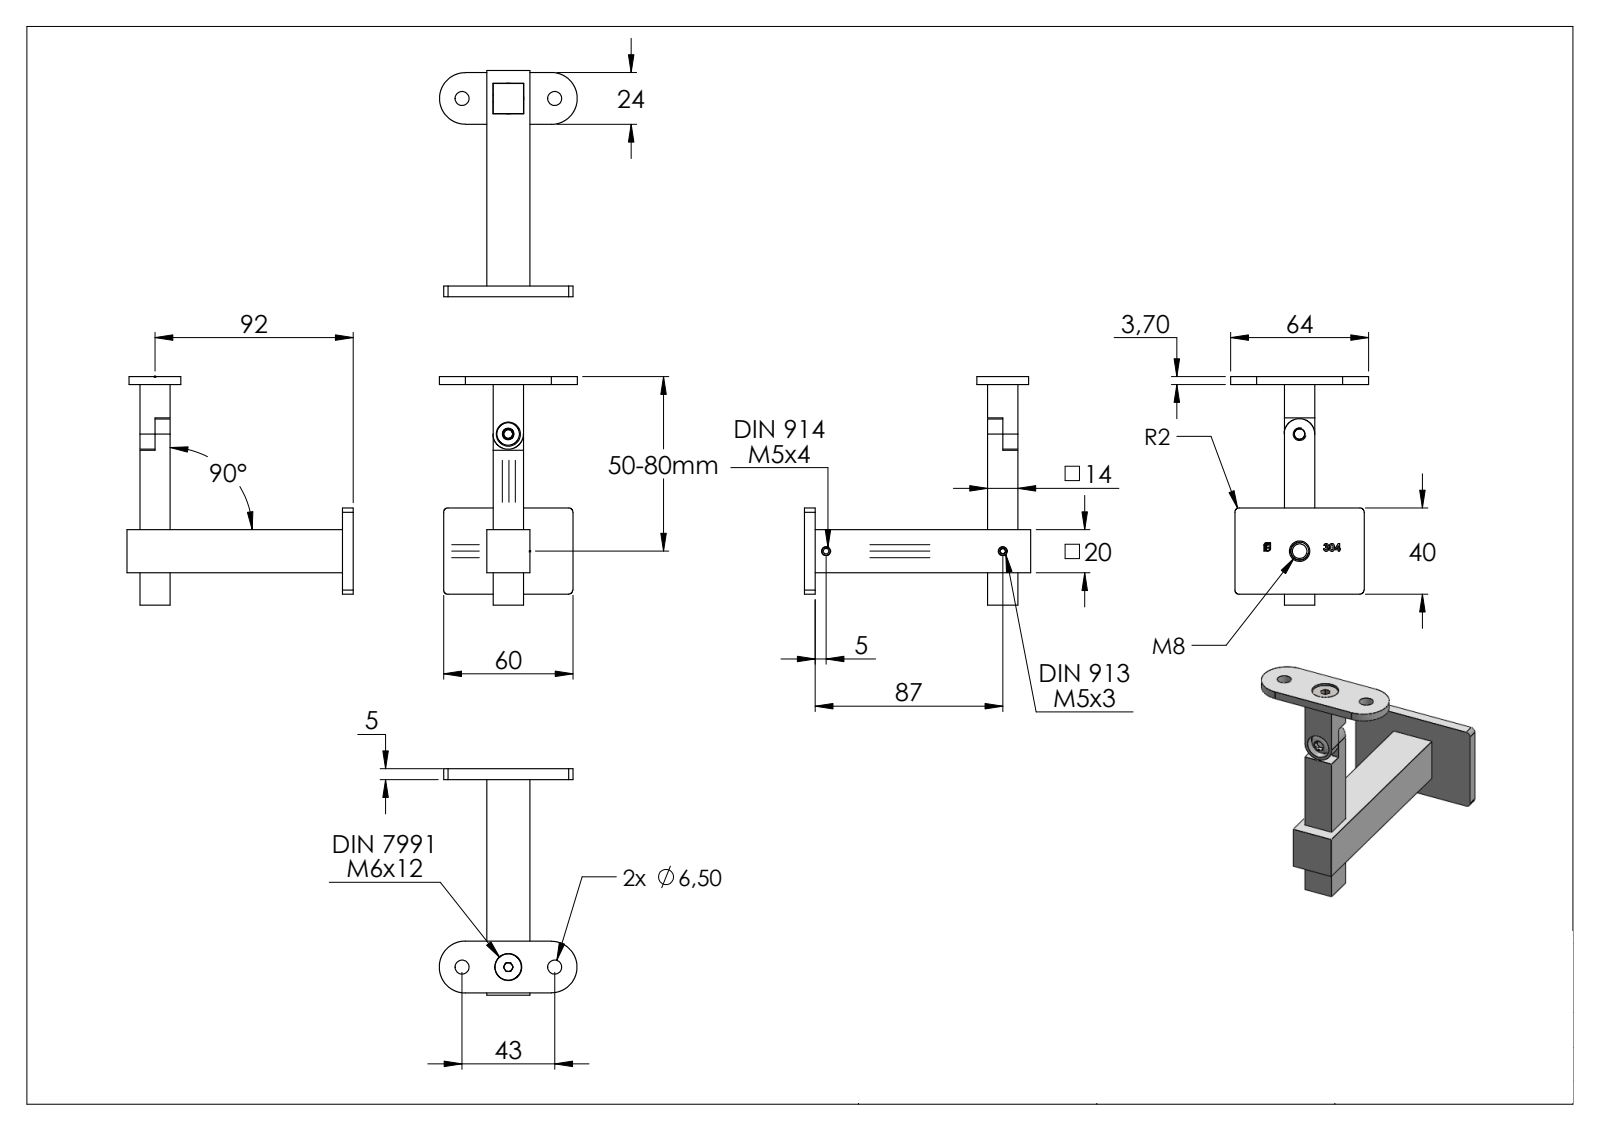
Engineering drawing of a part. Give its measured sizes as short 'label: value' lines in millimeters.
name: 51264-240 Teil5_51264-240 Teil5; 51264-240 Teil6; DIN914; 51264-240 (+8 more)
written by: SolidWorks 2018 (CONFIG_CONTROL_DESIGN)
unit: mm
bodies: 10 solids, 566 faces (267 planar, 89 cylindrical, 210 other)
size: 106 × 105 × 90
volume: 68 789 mm³; area: 29 773 mm²
holes: 3× ⌀6.5, 2× ⌀4.2, 2× ⌀5, 1× ⌀6.8, 1× ⌀8.2, 1× ⌀8.5, 1× ⌀11.2, 1× ⌀12.5, 1× ⌀14.1, 1× ⌀14.2
bosses: 2× ⌀14, 2× ⌀6, 2× ⌀5, 1× ⌀12, 1× ⌀10.5
rounds: 4× R2, 2× R12, 1× R6.5, 1× R7.15
face distances: 20, 5, 3, 17, 14, 80, 99, 85, 94, 87.3
hole spacings: 21.5, 43, 54.3, 82
